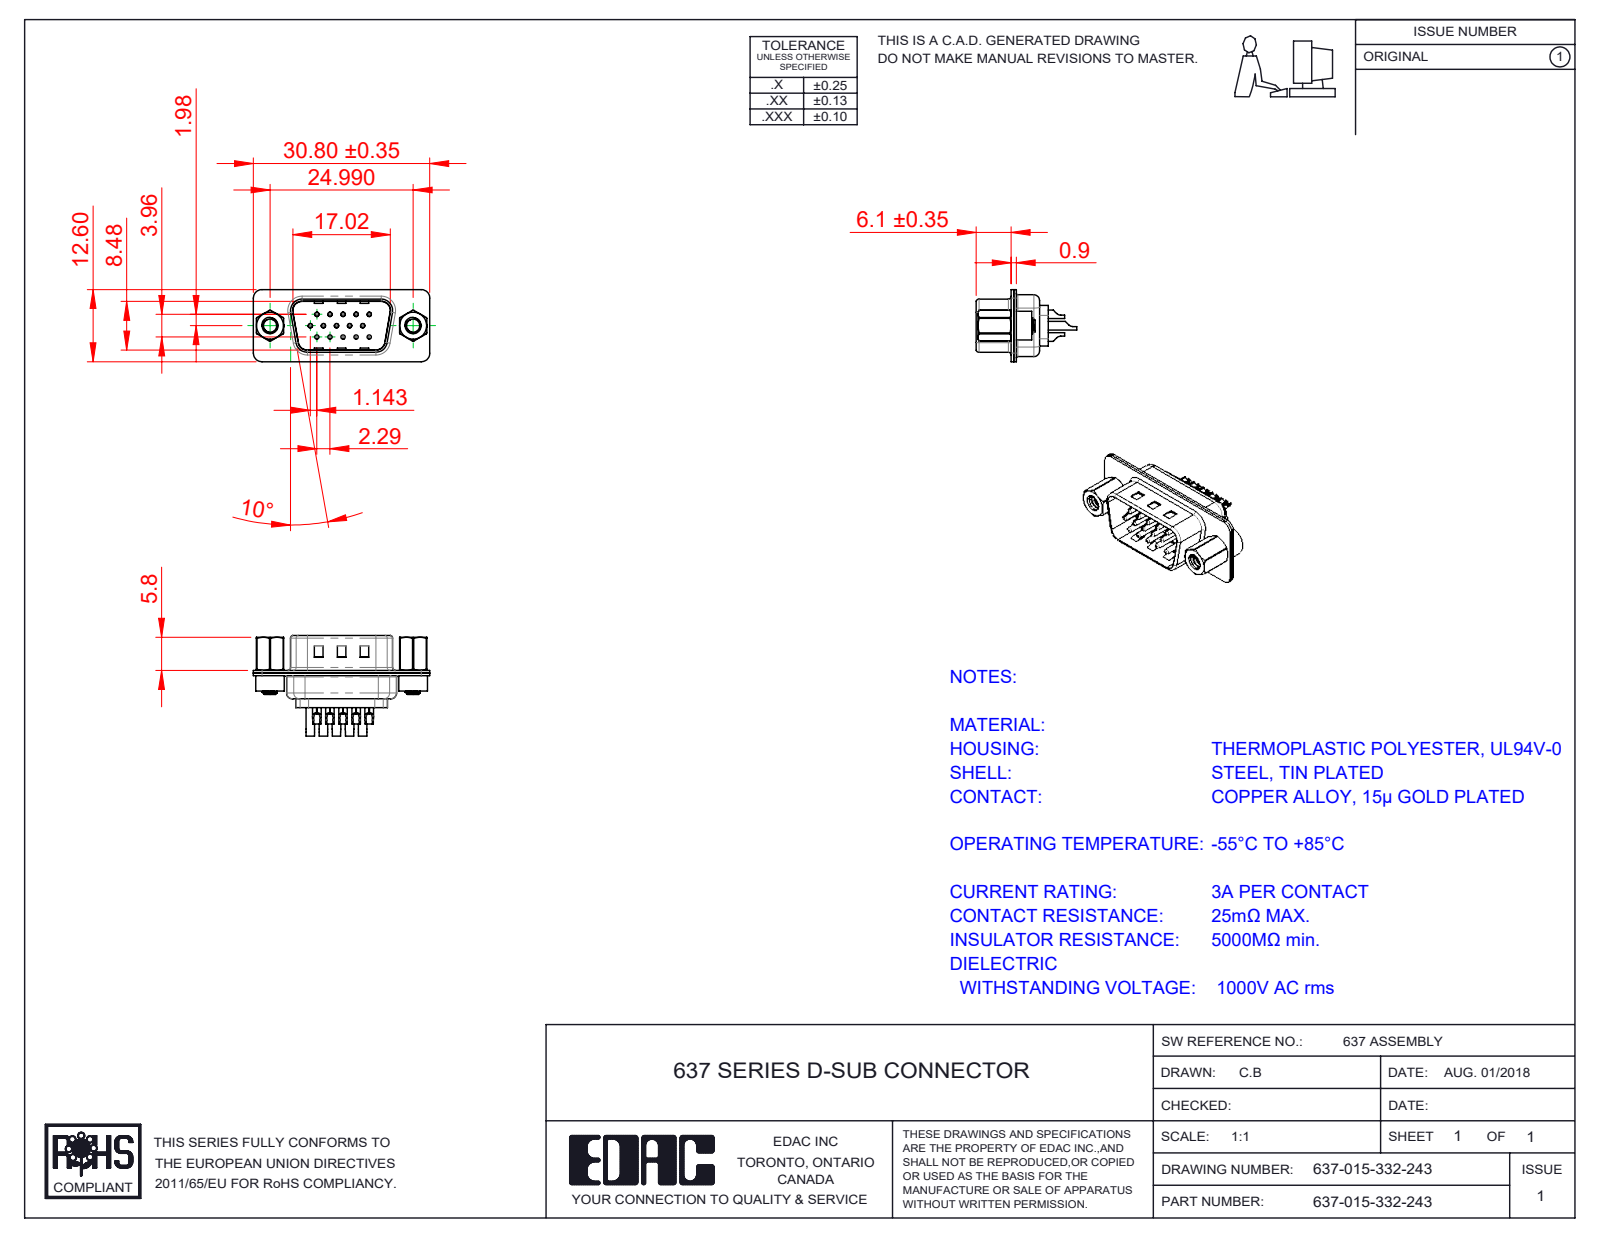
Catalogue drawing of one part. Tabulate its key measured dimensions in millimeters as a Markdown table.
| quantity | value |
| --- | --- |
| part name | 637 Housing_15 Contacts; 637 Shell Front_15 Contacts; 637 4-40 Hex Standoff; 637-015-332-263 (+5 more) |
| STEP written by | SolidWorks 2020 (CONFIG_CONTROL_DESIGN) |
| units | millimeters |
| bodies | 22 solids, 1390 faces (339 planar, 636 cylindrical, 415 other) |
| overall size | 30.8 × 17.55 × 12.6 |
| volume | 1 544 mm³ |
| surface area | 5 262 mm² |
| round holes (diameter × count) | 0.35 × 15, 1.1 × 15, 1.6 × 15, 2.26 × 2, 2.29 × 2, 4 × 2, 4.8 × 2 |
| round bosses / shafts (diameter × count) | 2 × 15, 1.5 × 15, 0.75 × 15, 5 × 2, 4.9 × 2, 2.79 × 2 |
| partial cylindrical surfaces (radius × count) | 1.5 × 16, 2 × 12, 0.5 × 8, 1 × 7, 0.25 × 4, 0.55 × 4, 0.7 × 4, 0.95 × 4 |
| main face-to-face distances | 0.45, 0.9, 0.4, 0.7, 8.88, 8.48, 1.05, 0.31, 4.55, 6.5 |
| hole center spacings | 3.96, 2.28, 4.57, 2.29, 6.05, 6.86, 7.92, 6.04 |
